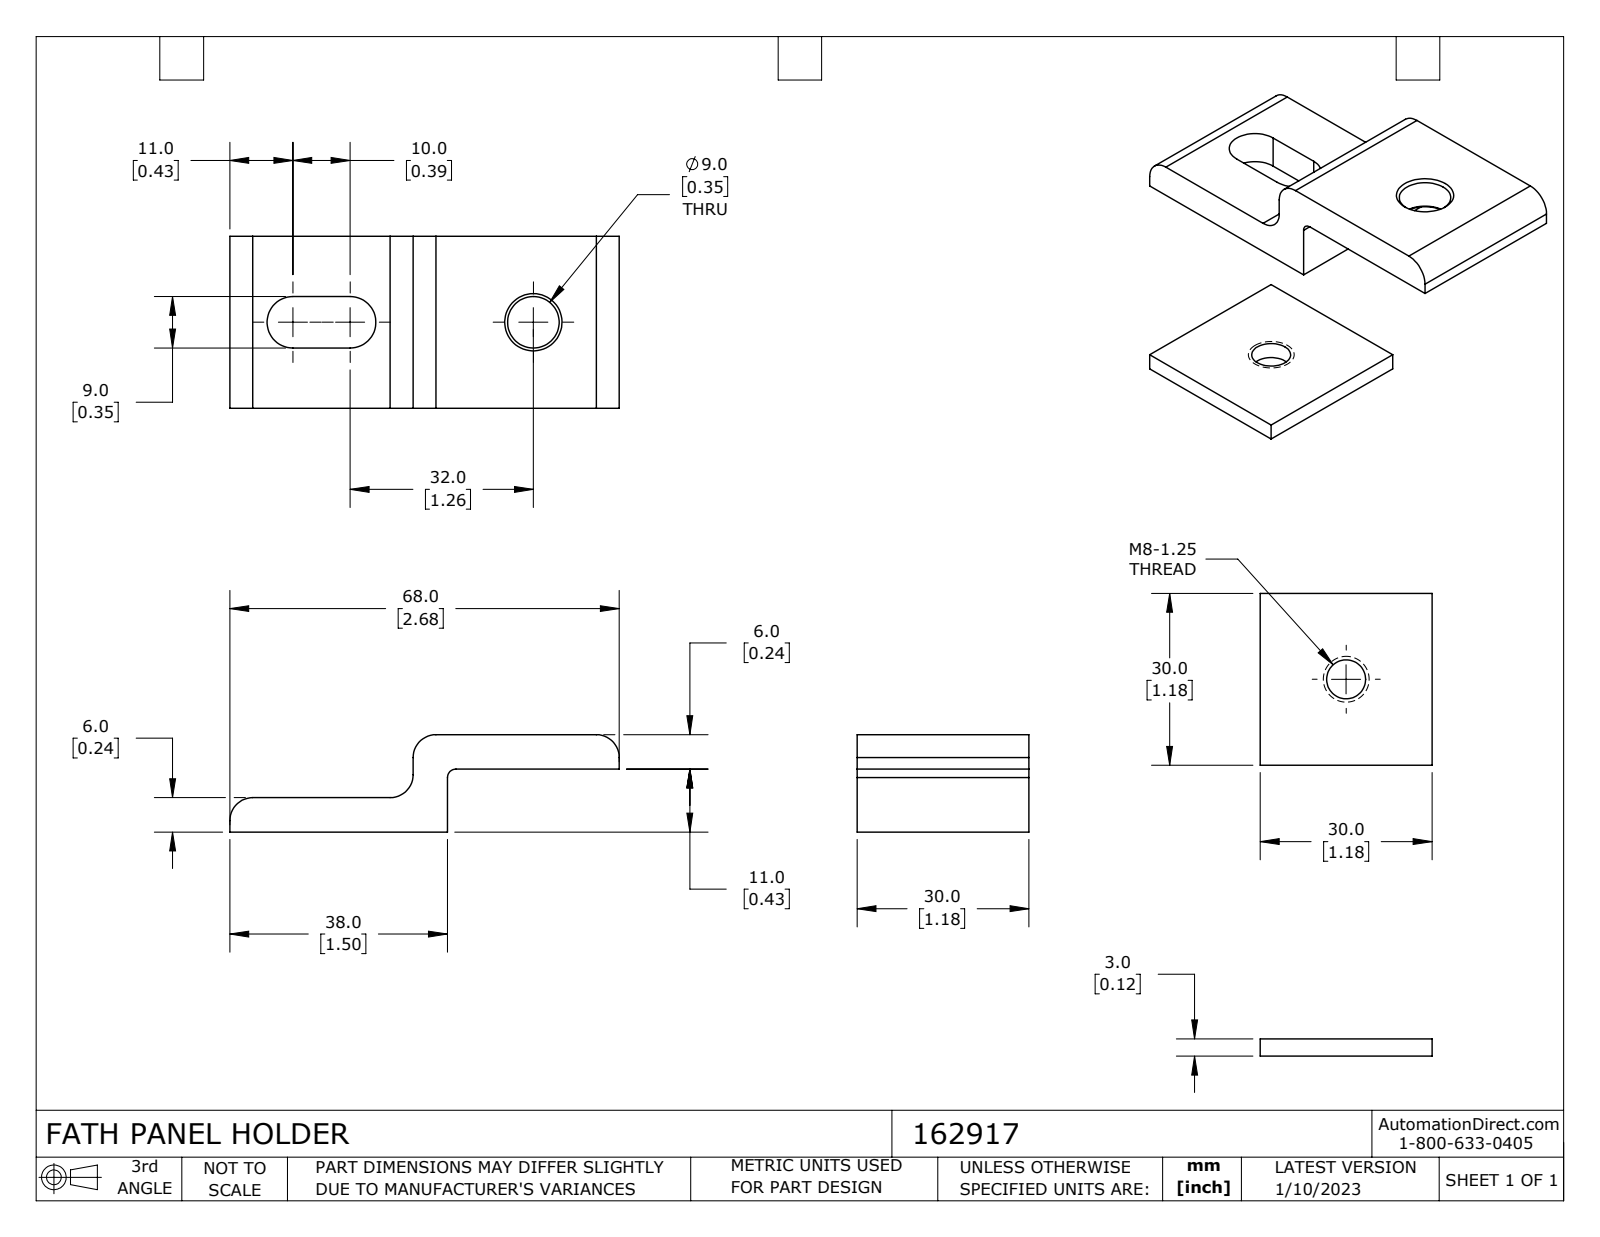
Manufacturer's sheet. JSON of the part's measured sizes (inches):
{"part_name": "162917", "step_written_by": "SolidWorks 2021 (CONFIG_CONTROL_DESIGN)", "units": "inches", "bodies": {"solids": 2, "faces": 33, "planar": 18, "cylindrical": 11, "other": 4}, "overall_size": [2.677, 2.209, 1.181], "volume_in3": 0.934, "surface_area_in2": 12.35, "round_holes": [[0.268, 1], [0.354, 1]], "partial_cylinders_radius": [[0.157, 4], [0.177, 2], [0.059, 1]], "face_to_face_distances": [0.236, 0.433, 1.421, 1.539, 0.118, 1.854, 1.972, 0.669, 2.091, 2.209], "hole_center_spacings": [1.496]}
